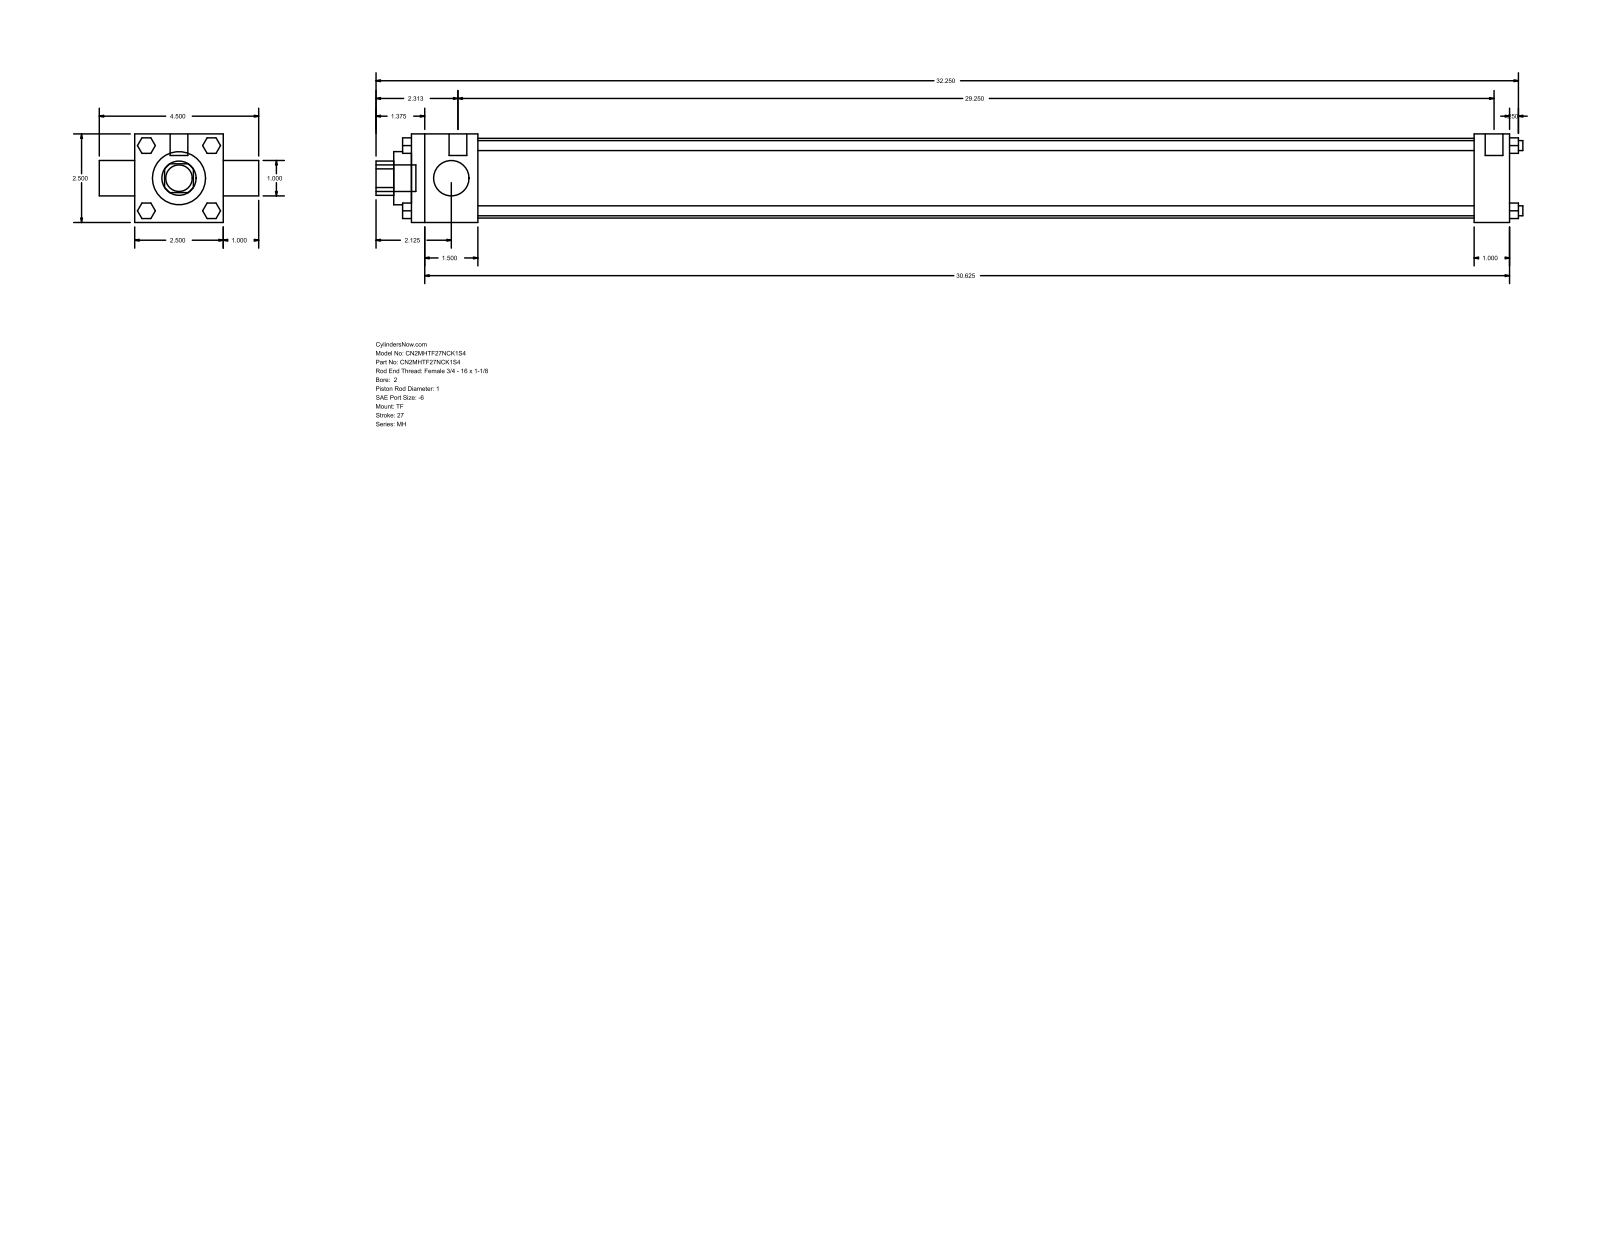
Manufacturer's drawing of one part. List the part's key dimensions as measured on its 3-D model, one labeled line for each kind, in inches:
Part name (STEP PRODUCT): MH_TF__0200_1
STEP written by: GSSL Pune (CONFIG_CONTROL_DESIGN)
Units: inches
Bodies: 0 solids, 120 faces (92 planar, 28 cylindrical, 0 other)
Overall size (bounding box): 32.375 × 4.5 × 2.5
Round holes (diameter × count): ⌀1 ×2, ⌀1.5 ×1, ⌀2.25 ×1
Round bosses / shafts (diameter × count): ⌀0.281 ×4, ⌀0.219 ×3, ⌀0.5 ×2, ⌀0.75 ×1
Partial cylindrical surfaces — rounded edges, fillets, slot ends (radius × count): R0.484 ×1
Main face-to-face distances: 2.5, 31, 1, 1.875, 30, 28.125, 29.125, 3.5, 31.5, 0.25
